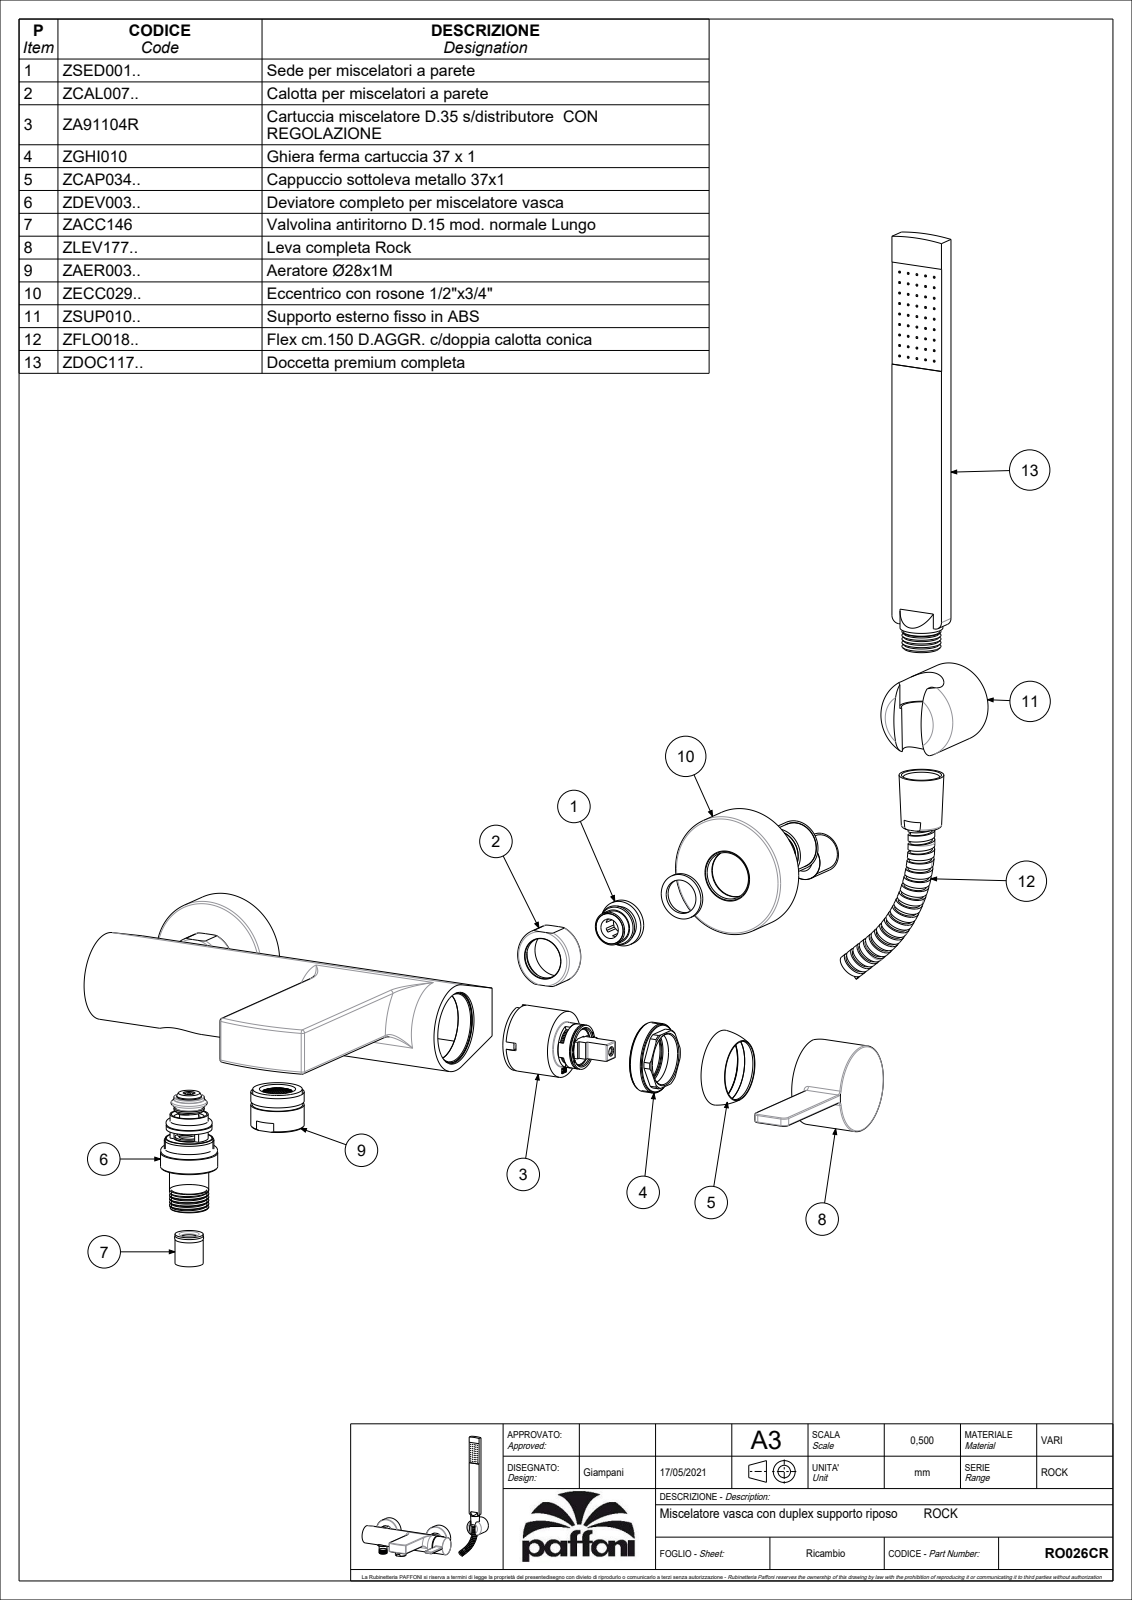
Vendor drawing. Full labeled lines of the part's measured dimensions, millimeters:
Part name (STEP PRODUCT): RO026CR
STEP written by: CREO PARAMETRIC BY PTC INC, 2020044 (CONFIG_CONTROL_DESIGN)
Units: millimetres
Bodies: 0 solids, 234 faces (67 planar, 54 cylindrical, 113 other)
Overall size (bounding box): 436 × 361.19 × 195.5
Round bosses / shafts (diameter × count): ⌀63.5 ×2, ⌀45.5 ×1, ⌀42 ×1, ⌀30 ×1, ⌀28 ×1, ⌀22.5 ×1, ⌀20.6 ×1, ⌀19 ×1
Partial cylindrical surfaces — rounded edges, fillets, slot ends (radius × count): R0.5 ×6, R1.5 ×6, R2 ×2, R3 ×2, R3.5 ×2, R15.6 ×2, R10 ×1, R23 ×1
Main face-to-face distances: 10, 8.5, 28.5, 38.5, 20, 18.5, 3, 15.5, 35.5, 7
